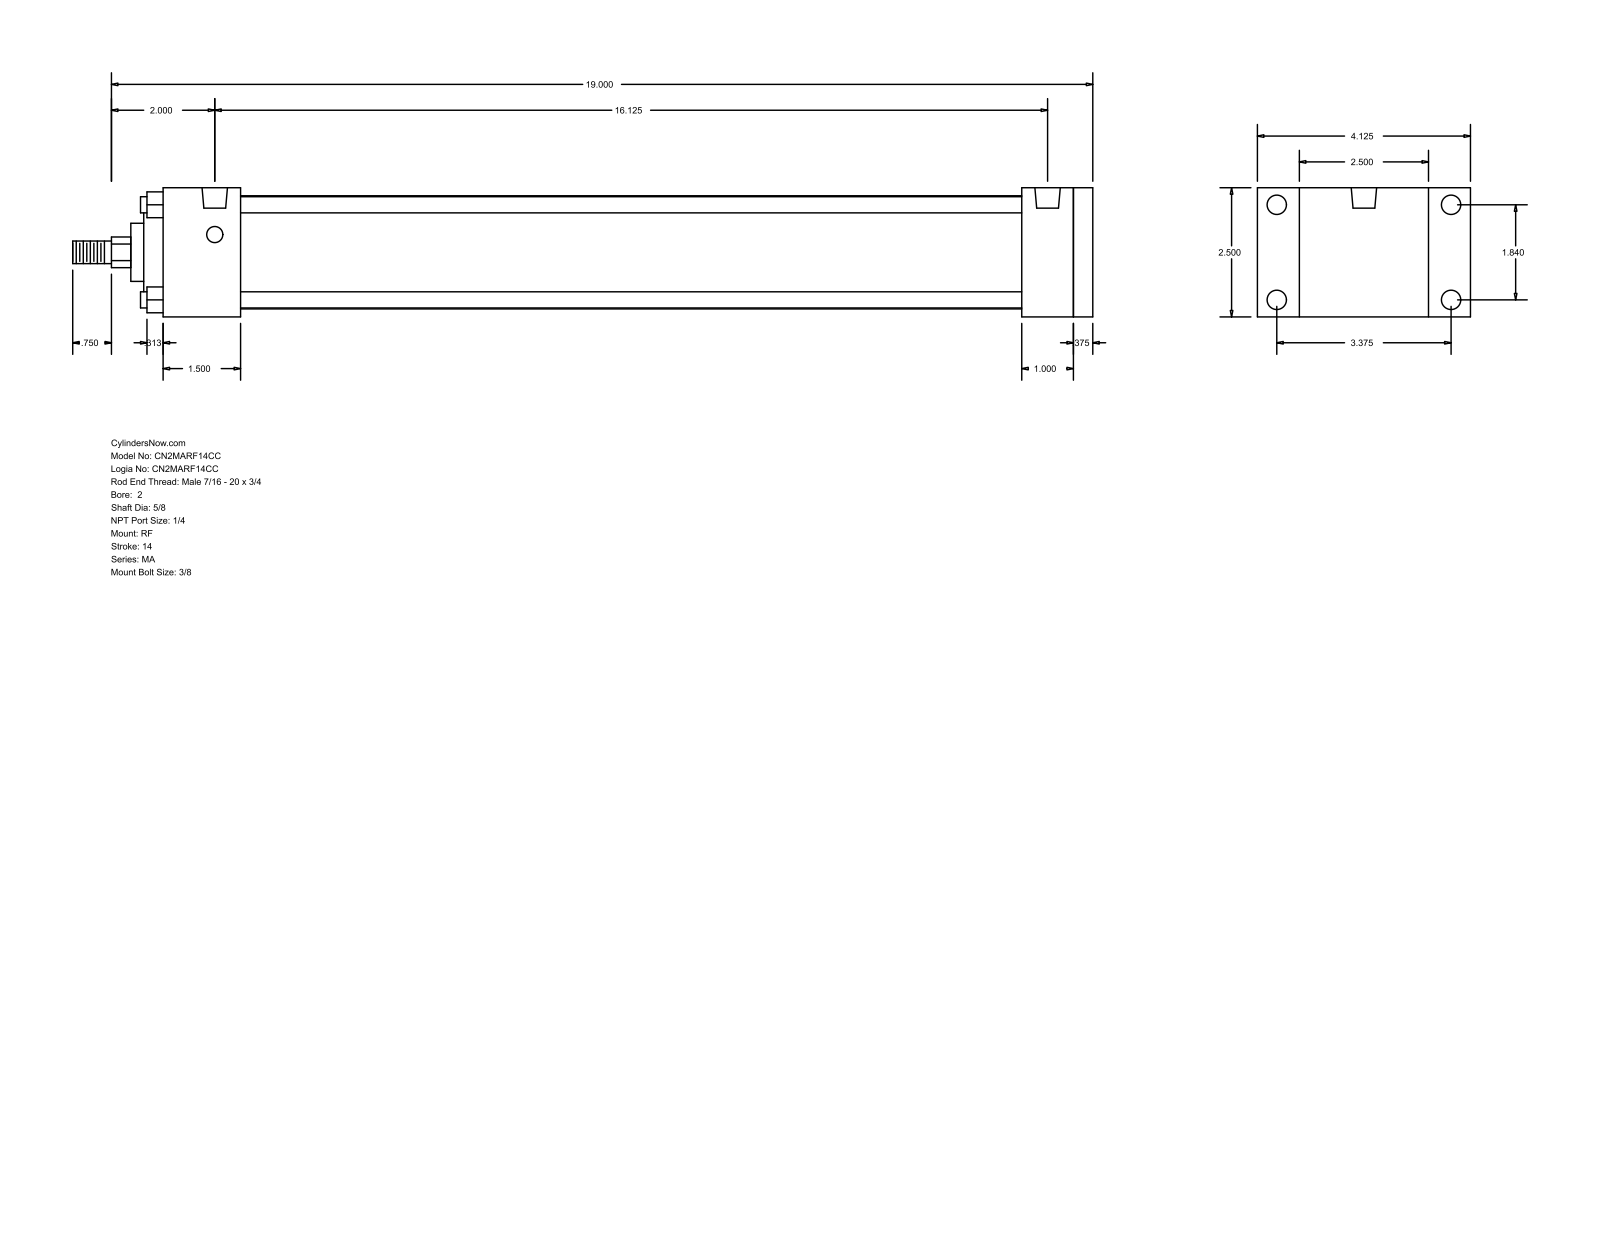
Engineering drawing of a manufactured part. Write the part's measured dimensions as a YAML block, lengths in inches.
part_name: "MA_RF__0200_0.625"
step_written_by: "GSSL Pune (CONFIG_CONTROL_DESIGN)"
units: inches
bodies: {solids: 0, faces: 94, planar: 65, cylindrical: 29, other: 0}
overall_size: [19.75, 4.125, 2.5]
round_holes:
  - {diameter: 0.313, count: 4}
  - {diameter: 0.375, count: 4}
  - {diameter: 0.492, count: 2}
round_bosses_or_shafts:
  - {diameter: 0.313, count: 4}
  - {diameter: 2.19, count: 1}
  - {diameter: 2, count: 1}
  - {diameter: 1.125, count: 1}
  - {diameter: 0.625, count: 1}
  - {diameter: 0.437, count: 1}
partial_cylinders:
  - {radius: 0.297, count: 1}
face_to_face_distances: [2.5, 0.375, 1.5, 17.625, 18, 18.375, 16.125, 16.5, 16.625, 15.125]
hole_center_spacings: [1.84, 3.375, 3.844, 16.125]
